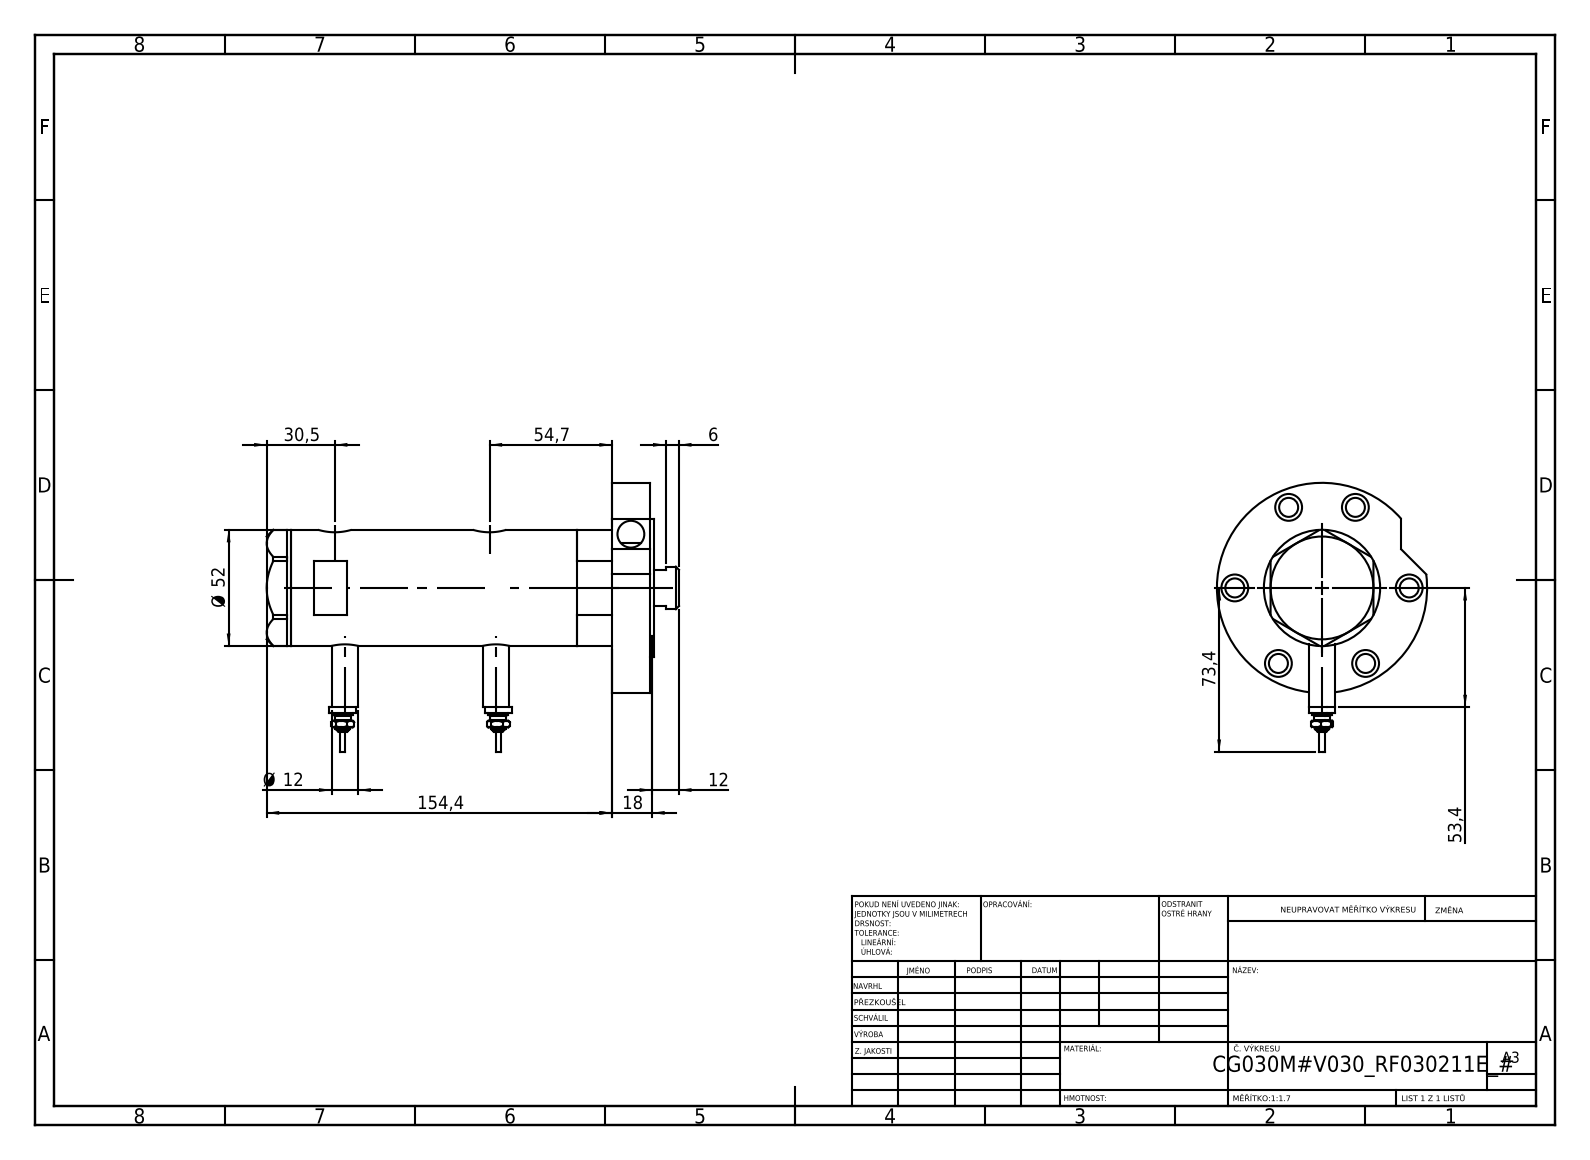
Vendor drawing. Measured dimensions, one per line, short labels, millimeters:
name: Switch; V270CG_MIDDLE; V270CG_BACK; V270CG_RF211E (+2 more)
written by: SolidWorks 2019 (CONFIG_CONTROL_DESIGN)
unit: mm
bodies: 7 solids, 270 faces (104 planar, 102 cylindrical, 64 other)
size: 184.4 × 120.4 × 94
volume: 422 746 mm³; area: 103 695 mm²
holes: 7× ⌀12, 6× ⌀8.5, 2× ⌀9.73, 2× ⌀12.5, 2× ⌀15, 1× ⌀6.5, 1× ⌀20, 1× ⌀21.5, 1× ⌀30, 1× ⌀33, 1× ⌀40, 1× ⌀44
bosses: 4× ⌀12, 2× ⌀9, 2× ⌀7, 2× ⌀4.5, 2× ⌀2.5, 1× ⌀94, 1× ⌀62, 1× ⌀52
face distances: 17, 143.4, 160.4, 2, 162.4, 91.5, 51.9, 68.9, 11, 173.4
hole spacings: 39, 43.34, 64.85, 67.55, 69.95, 77.83, 2.9, 4.5
